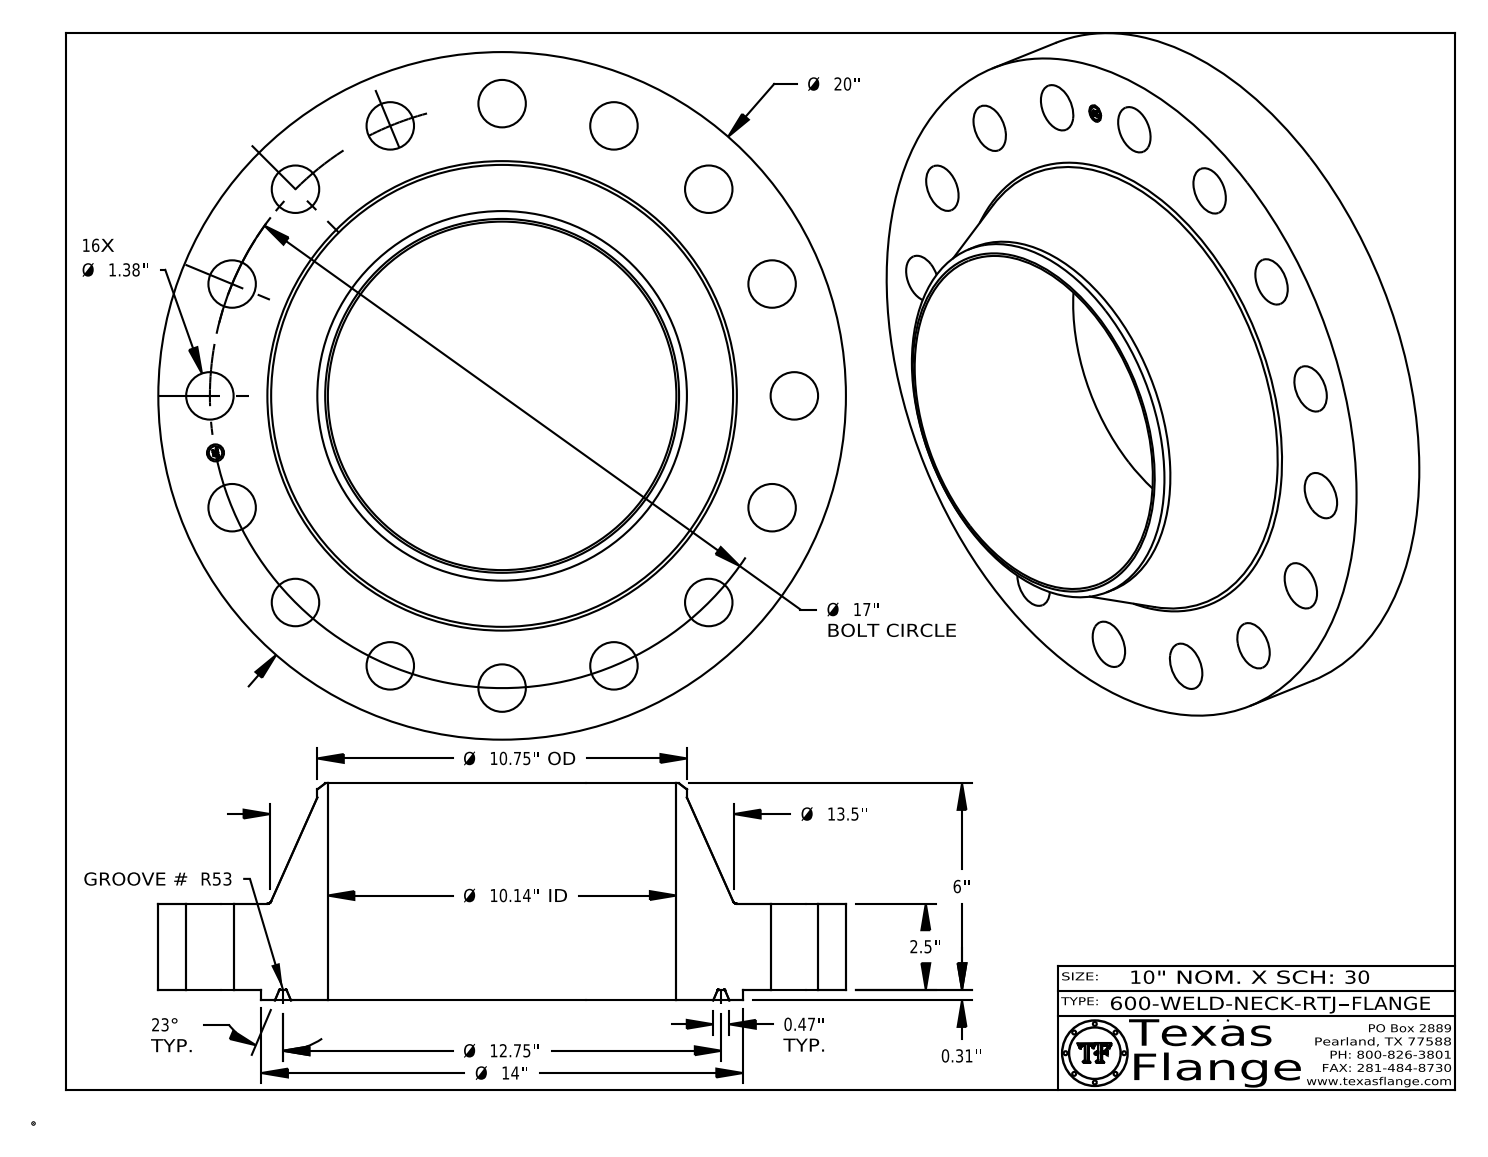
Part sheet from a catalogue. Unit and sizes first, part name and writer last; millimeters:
Units: millimetres
Overall size (bounding box): 508 × 508 × 160.4
Round holes (diameter × count): ⌀35.1 ×16, ⌀12.6 ×1, ⌀257.5 ×1
Round bosses / shafts (diameter × count): ⌀0.8 ×8, ⌀508 ×1, ⌀355.6 ×1, ⌀273.1 ×1, ⌀9.9 ×1
Main face-to-face distances: 63.5, 8, 71.5, 160.4, 152.4, 88.9, 71.1, 63.1, 0.4, 89.3
Hole centre spacings: 84.3, 359, 215.9, 165.3, 305.3, 239.9, 239.9, 398.9
Volume: 10 730 000 mm³ · Surface area: 687 700 mm²
Bodies: 1 solid, 445 faces (371 planar, 60 cylindrical, 14 other)
Part name (STEP PRODUCT): 600-WELD-NECK-RTJ
STEP written by: CATIA V5 STEP AP214 (AUTOMOTIVE_DESIGN)
